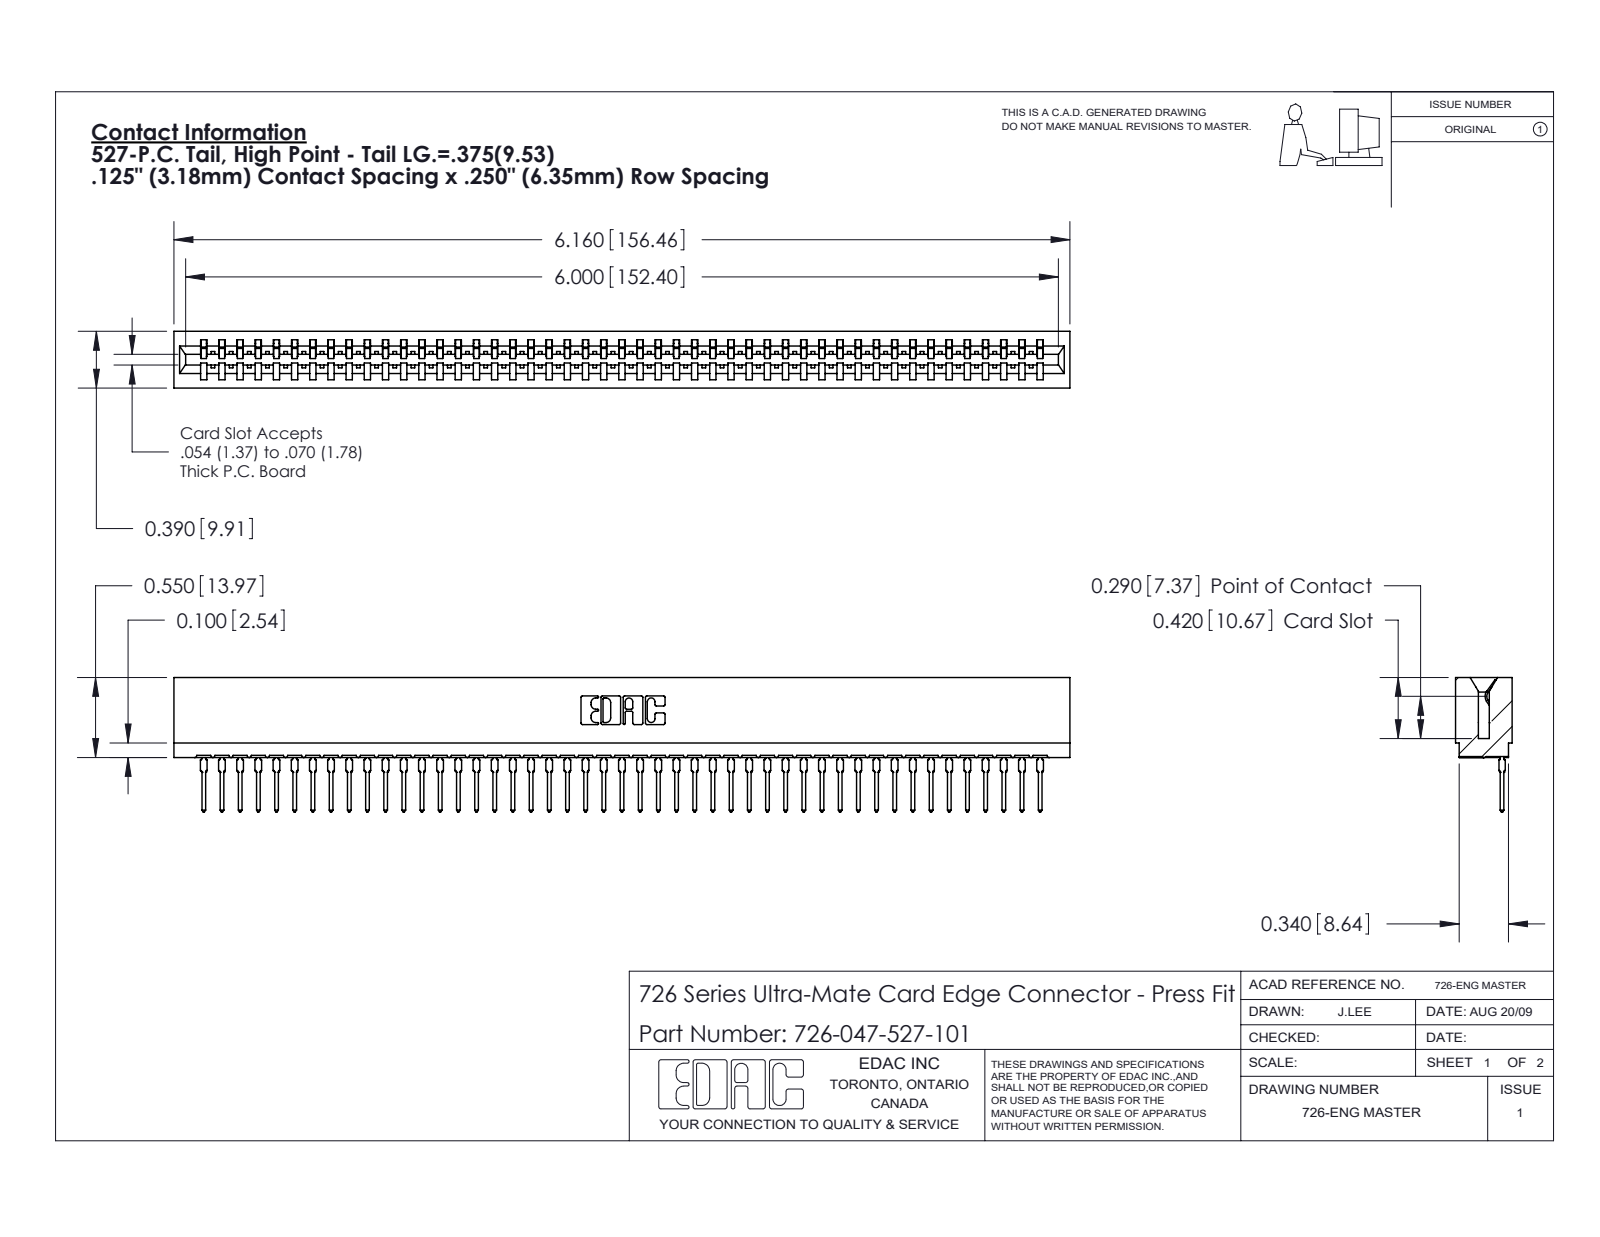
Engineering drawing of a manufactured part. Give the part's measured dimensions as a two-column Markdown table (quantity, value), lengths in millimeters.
| quantity | value |
| --- | --- |
| part name | 726 Part_.515 Slot Depth - 01; 746-292-001_527; 726-047-527-101 |
| STEP written by | SolidWorks 2020 (CONFIG_CONTROL_DESIGN) |
| units | millimeters |
| bodies | 48 solids, 5173 faces (3016 planar, 935 cylindrical, 1222 other) |
| overall size | 156.5 × 23.5 × 9.9 |
| volume | 14 000 mm³ |
| surface area | 21 690 mm² |
| partial cylindrical surfaces (radius × count) | 0.5 × 94, 0.4 × 48, 0.3 × 22, 0.2 × 6, 0.8 × 6, 0.1 × 4, 0.3 × 4, 0.7 × 3 |
| main face-to-face distances | 1.4, 8.5, 9.9, 0.6, 7.8, 6.4, 2.1, 7, 9.3, 0.8 |
